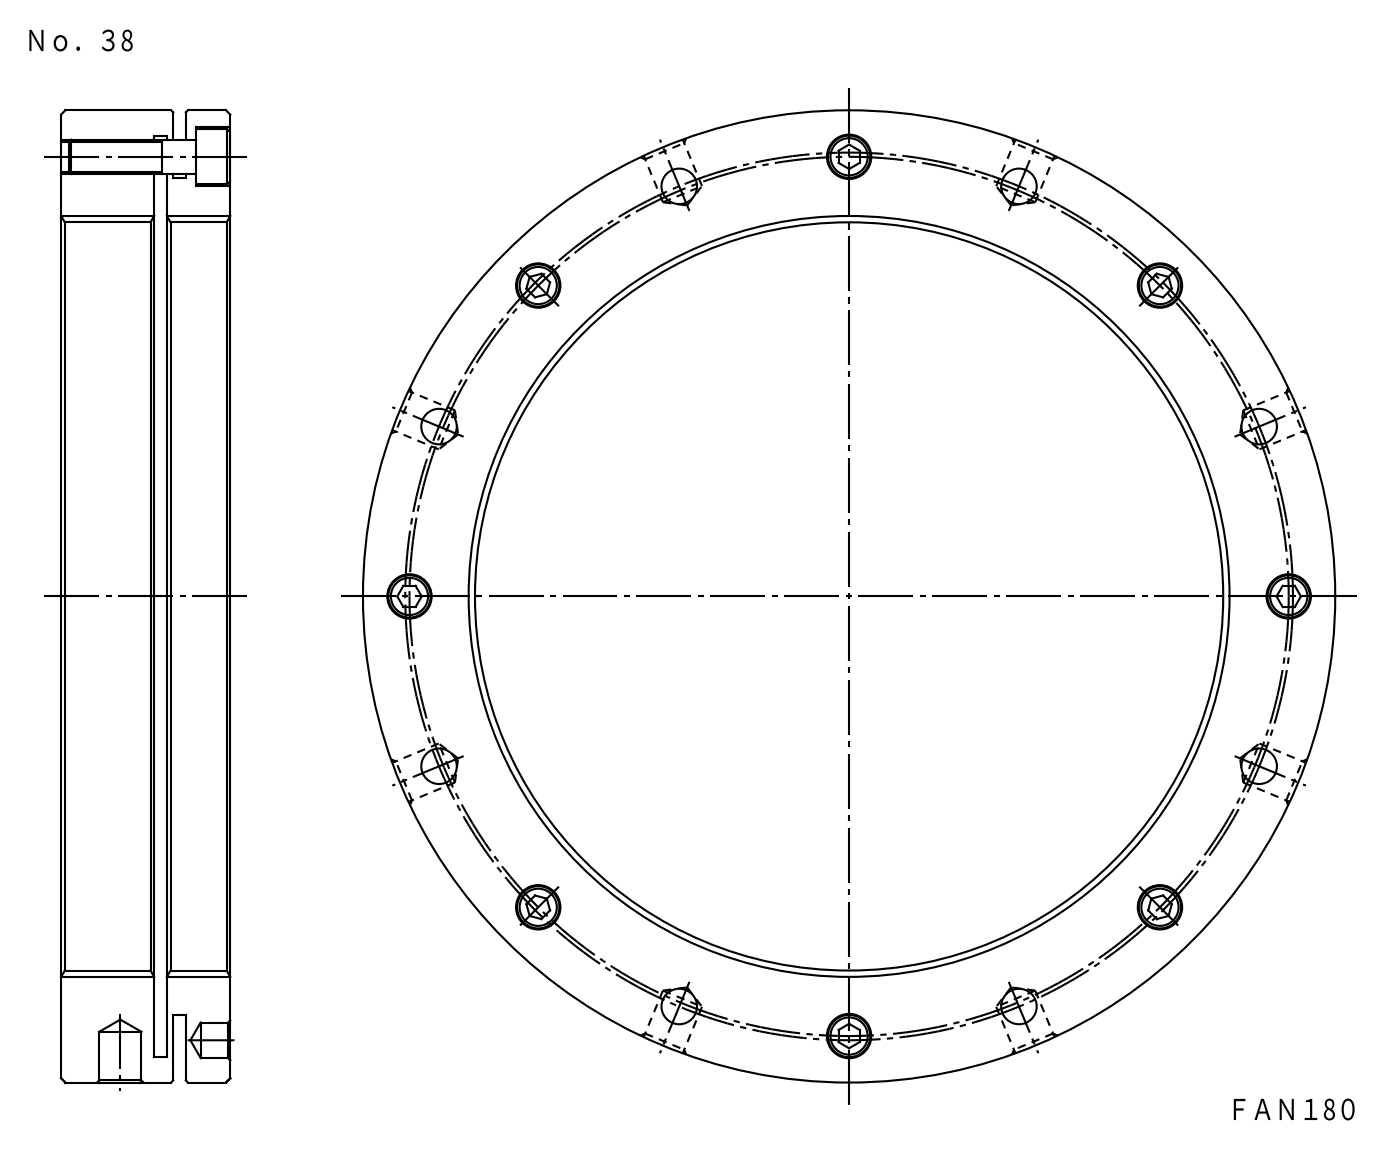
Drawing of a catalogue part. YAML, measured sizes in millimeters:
part_name: "FKD FAN180; M8X30_default"
step_written_by: "SolidWorks 2012 (CONFIG_CONTROL_DESIGN)"
units: millimeters
bodies: {solids: 9, faces: 266, planar: 94, cylindrical: 140, other: 32}
overall_size: [230, 230, 40]
volume: 566159
surface_area: 150098
round_holes:
  - {diameter: 8.4, count: 8}
  - {diameter: 8.6, count: 8}
  - {diameter: 10, count: 8}
  - {diameter: 14, count: 8}
  - {diameter: 6.65, count: 7}
  - {diameter: 6.65, count: 1}
  - {diameter: 180, count: 1}
  - {diameter: 218, count: 1}
round_bosses_or_shafts:
  - {diameter: 13, count: 8}
  - {diameter: 8, count: 8}
  - {diameter: 230, count: 1}
  - {diameter: 198, count: 1}
face_to_face_distances: [3, 4.5, 40, 22, 18, 25, 15, 26.5, 1.5, 13.5]
hole_center_spacings: [116.12, 173.78, 204.99, 40.78, 40.79, 79.6, 104, 105]
